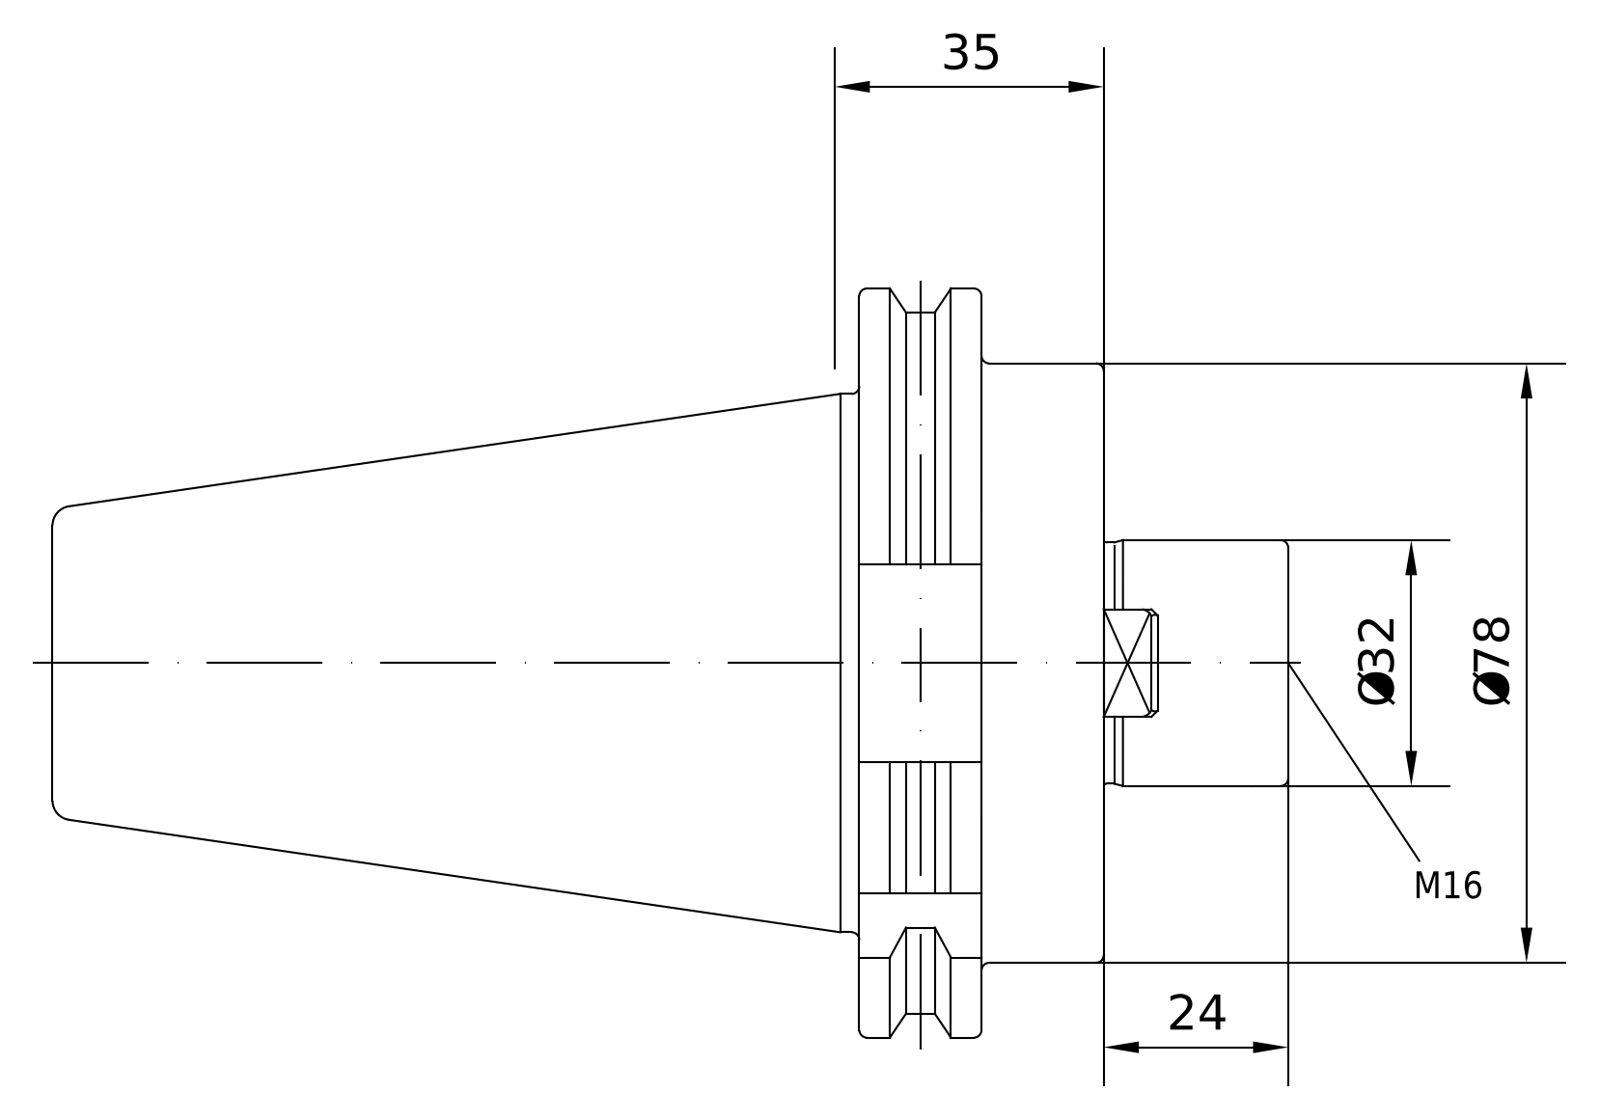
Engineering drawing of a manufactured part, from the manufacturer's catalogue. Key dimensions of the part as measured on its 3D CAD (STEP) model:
Part name (STEP PRODUCT): 50-350-32
STEP written by: PRO/ENGINEER BY PARAMETRIC TECHNOLOGY CORPORATION, 2010430 (CONFIG_CONTROL_DESIGN)
Units: millimetres
Bodies: 1 solid, 112 faces (35 planar, 28 cylindrical, 49 other)
Overall size (bounding box): 160.6 × 97.47 × 94
Volume: 429 891 mm³ · Surface area: 53 090 mm²
Round holes (diameter × count): ⌀14 ×1, ⌀16 ×1, ⌀20.75 ×1, ⌀25.01 ×1, ⌀25.7 ×1
Round bosses / shafts (diameter × count): ⌀91 ×1, ⌀78 ×1, ⌀69.15 ×1, ⌀32 ×1, ⌀24.01 ×1
Partial cylindrical surfaces — rounded edges, fillets, slot ends (radius × count): R1.75 ×1, R48.74 ×1
Main face-to-face distances: 31.8, 15.85, 15.95, 72.8, 55.8, 39.95, 24, 38.8, 22.95, 7
